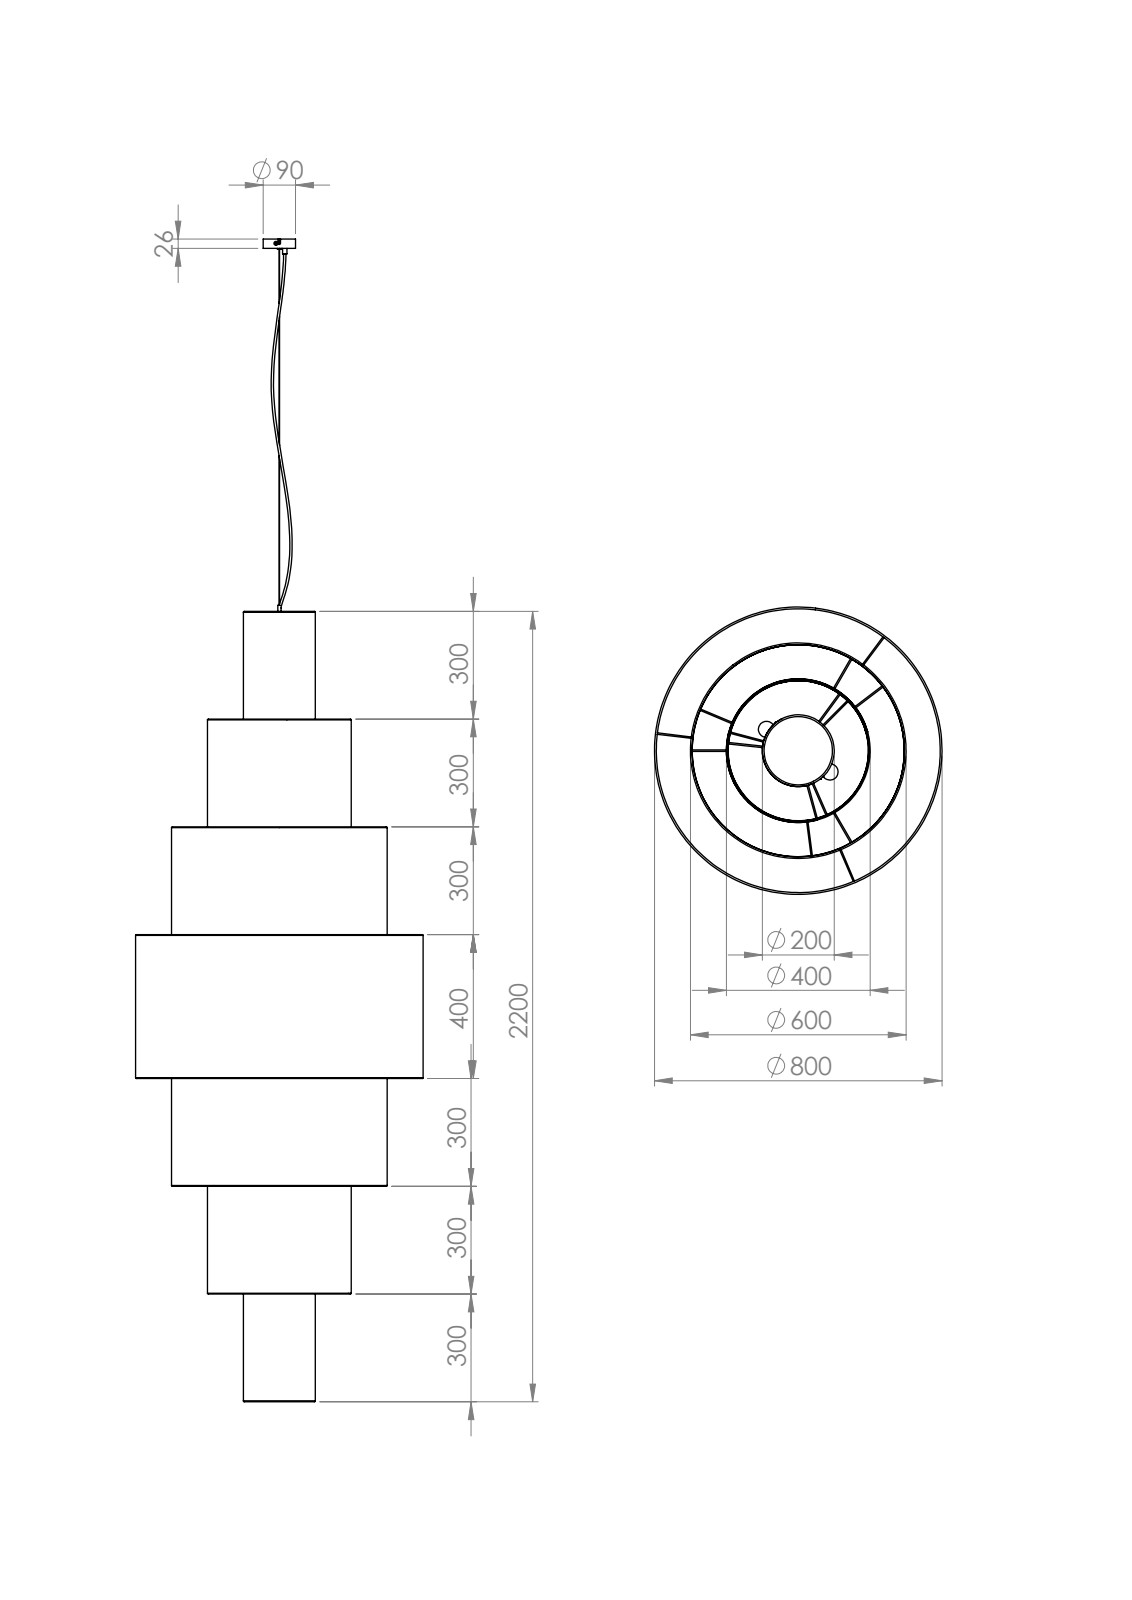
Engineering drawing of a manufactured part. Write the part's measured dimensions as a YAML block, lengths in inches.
part_name: "Rosett_longer; FLY SC080220 kuppel D600; FLY kuppel D200; Juhtmelukk (+8 more)"
step_written_by: "SolidWorks 2018 (AUTOMOTIVE_DESIGN)"
units: inches
bodies: {solids: 70, faces: 685, planar: 204, cylindrical: 245, other: 236}
overall_size: [127.464, 31.496, 31.496]
volume: 195.5
surface_area: 12660
round_holes:
  - {diameter: 0.354, count: 6}
  - {diameter: 1.063, count: 4}
  - {diameter: 0.315, count: 3}
  - {diameter: 0.353, count: 2}
  - {diameter: 0.098, count: 1}
  - {diameter: 0.197, count: 1}
  - {diameter: 0.394, count: 1}
  - {diameter: 3.386, count: 1}
  - {diameter: 7.835, count: 1}
  - {diameter: 15.709, count: 1}
  - {diameter: 23.583, count: 1}
  - {diameter: 31.457, count: 1}
round_bosses_or_shafts:
  - {diameter: 0.157, count: 18}
  - {diameter: 1.575, count: 4}
  - {diameter: 0.315, count: 4}
  - {diameter: 0.63, count: 3}
  - {diameter: 0.236, count: 3}
  - {diameter: 0.472, count: 2}
  - {diameter: 0.413, count: 2}
  - {diameter: 31.496, count: 1}
partial_cylinders:
  - {radius: 0.197, count: 10}
  - {radius: 0.118, count: 5}
  - {radius: 0.079, count: 4}
  - {radius: 0.315, count: 4}
  - {radius: 0.029, count: 2}
  - {radius: 0.108, count: 2}
face_to_face_distances: [0.157, 86.142, 86.299, 85.984, 42.362, 43.937, 42.205, 43.78, 0.079, 126.263]
hole_center_spacings: [2.333, 4.666, 0.591, 1.181, 1.743, 2.924]
